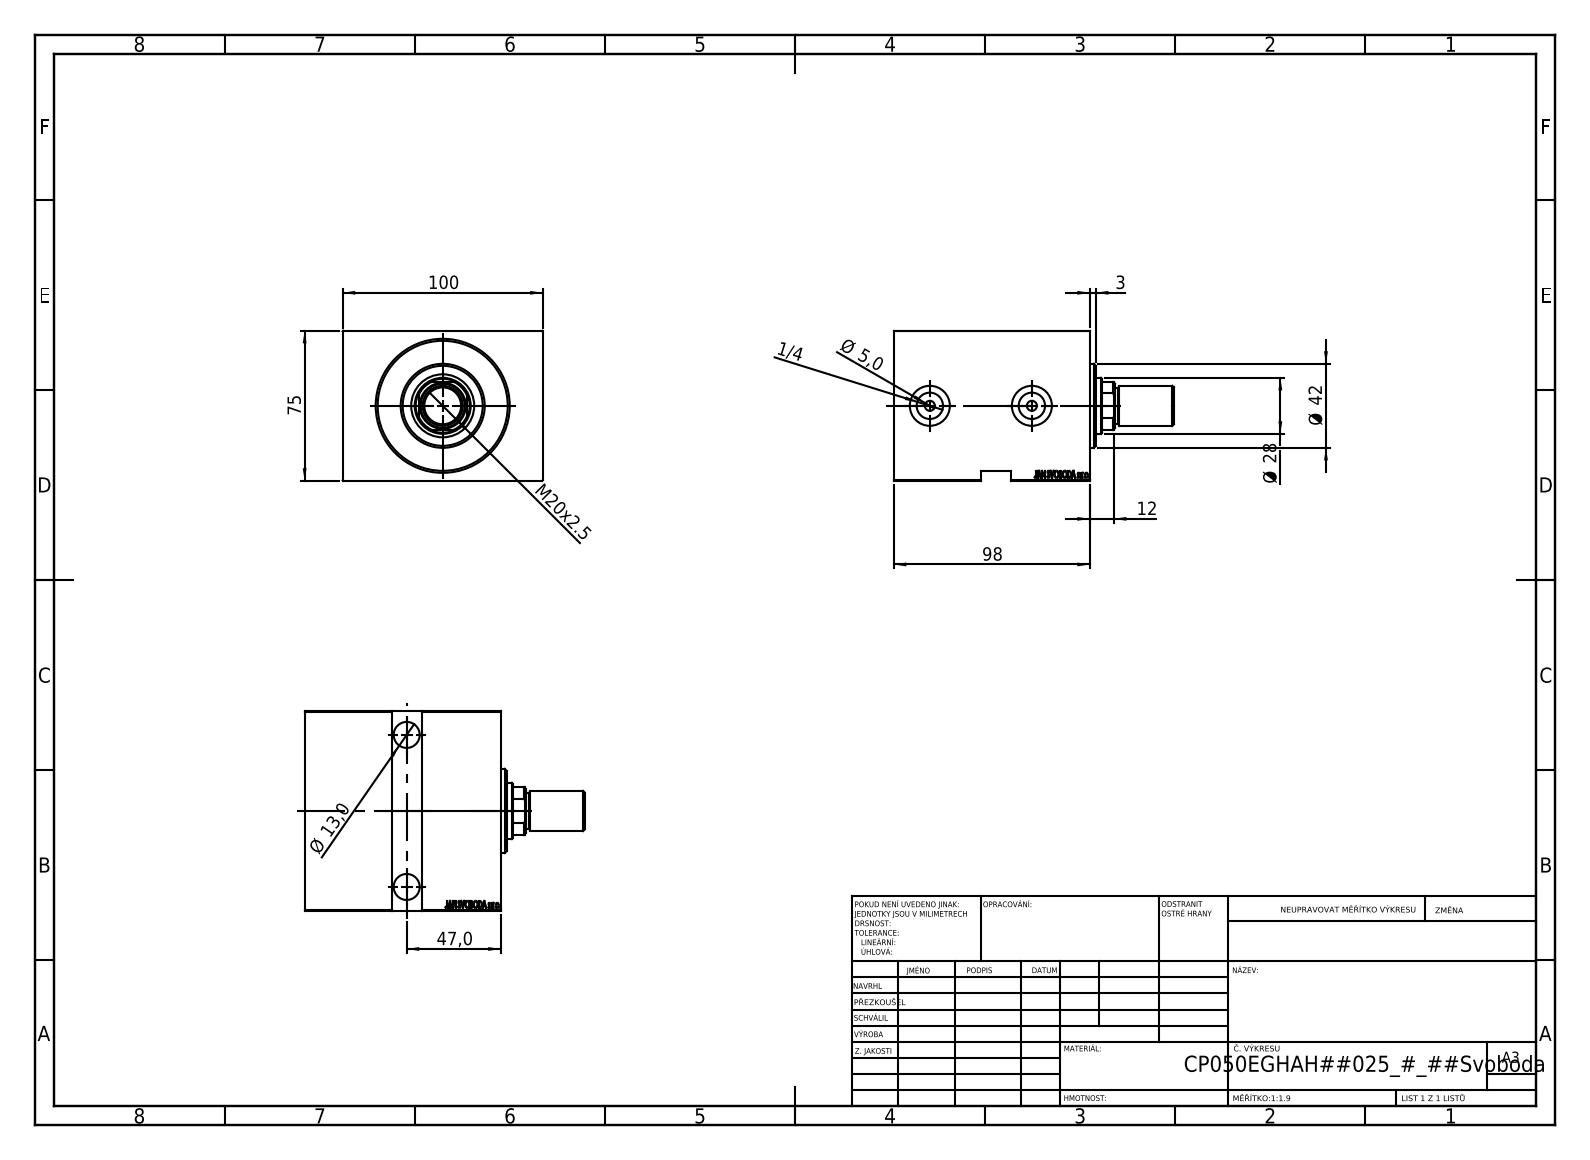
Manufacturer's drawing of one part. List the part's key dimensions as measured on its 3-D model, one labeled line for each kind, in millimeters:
Part name (STEP PRODUCT): V450CM_E_VCP; V450CM_E_Body; V450CM_MALE_METRIC; V450CM_VC_B
STEP written by: SolidWorks 2019 (CONFIG_CONTROL_DESIGN)
Units: millimetres
Bodies: 4 solids, 860 faces (412 planar, 48 cylindrical, 400 other)
Overall size (bounding box): 140 × 100 × 75
Volume: 683 332 mm³ · Surface area: 101 138 mm²
Round holes (diameter × count): ⌀5 ×2, ⌀13 ×2, ⌀13.16 ×2, ⌀19 ×2, ⌀20 ×2, ⌀18.5 ×1, ⌀28 ×1, ⌀31.5 ×1, ⌀50 ×1, ⌀65 ×1
Round bosses / shafts (diameter × count): ⌀52 ×1, ⌀42 ×1, ⌀20 ×1, ⌀18 ×1
Partial cylindrical surfaces — rounded edges, fillets, slot ends (radius × count): R13.5 ×1
Main face-to-face distances: 75, 100, 98, 14, 84, 5, 79, 93, 47, 81.4
Hole centre spacings: 51, 76
